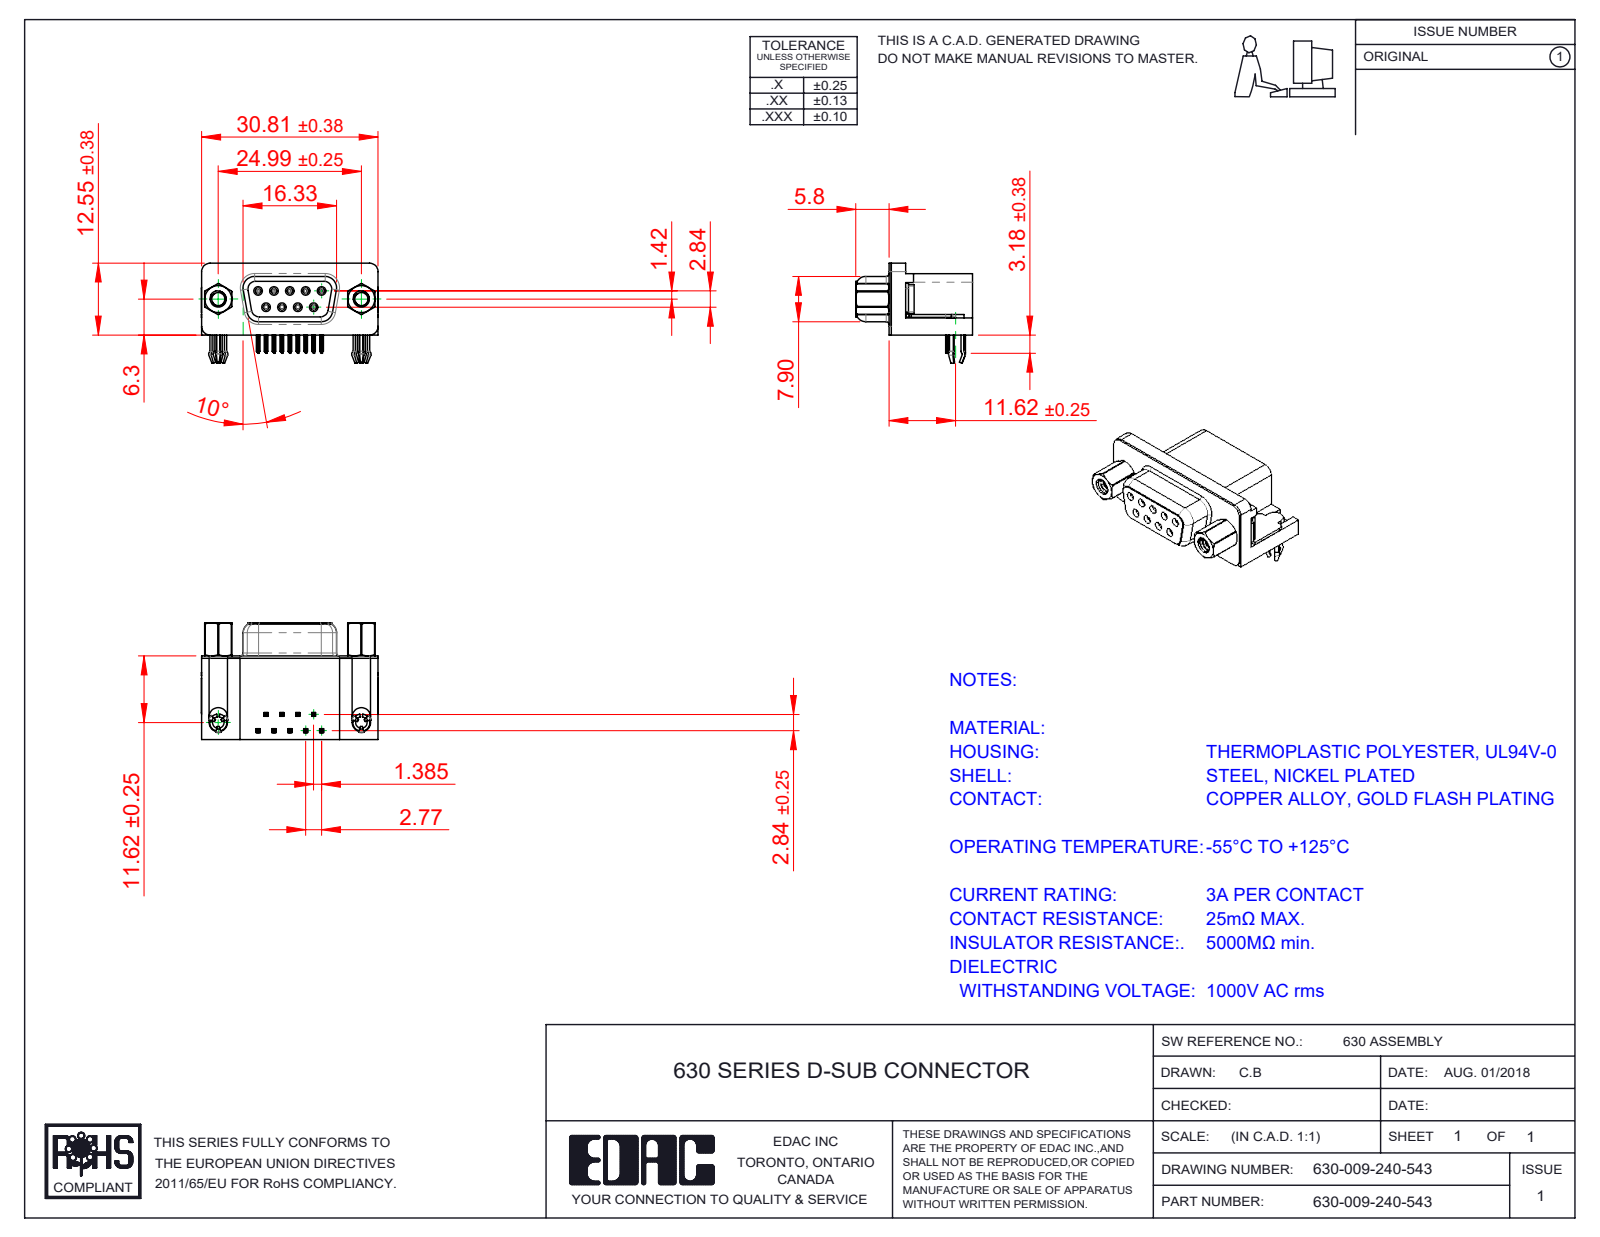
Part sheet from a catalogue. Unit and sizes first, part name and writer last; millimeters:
Units: millimetres
Overall size (bounding box): 30.89 × 20.4 × 17.48
Round holes (diameter × count): ⌀0.8 ×9, ⌀0.9 ×9, ⌀2 ×2, ⌀2.26 ×2, ⌀2.29 ×2, ⌀4 ×2, ⌀4.8 ×2, ⌀5 ×2
Round bosses / shafts (diameter × count): ⌀1.2 ×9, ⌀4.9 ×2, ⌀4.75 ×2, ⌀3.9 ×2, ⌀3 ×2, ⌀2.79 ×2
Partial cylindrical surfaces — rounded edges, fillets, slot ends (radius × count): R0.1 ×72, R0.15 ×36, R0.35 ×18, R1 ×18, R0.25 ×12, R0.34 ×9, R1.35 ×8, R1.6 ×8
Main face-to-face distances: 0.4, 14.6, 14.2, 6.2, 10.34, 5.8, 2.9, 2.5, 11.7, 0.35
Hole centre spacings: 3.16, 2.77, 5.54, 5.03, 5.04, 8.31, 7.48, 7.49
Volume: 4 427 mm³ · Surface area: 5 991 mm²
Bodies: 17 solids, 1800 faces (742 planar, 494 cylindrical, 564 other)
Part name (STEP PRODUCT): 630 4-40 Hex Standoff 5; 630 4-40 Threaded Rivet; 630 Housing_09 Socket; 630 Contact Bottom (+4 more)
STEP written by: SolidWorks 2020 (CONFIG_CONTROL_DESIGN)
